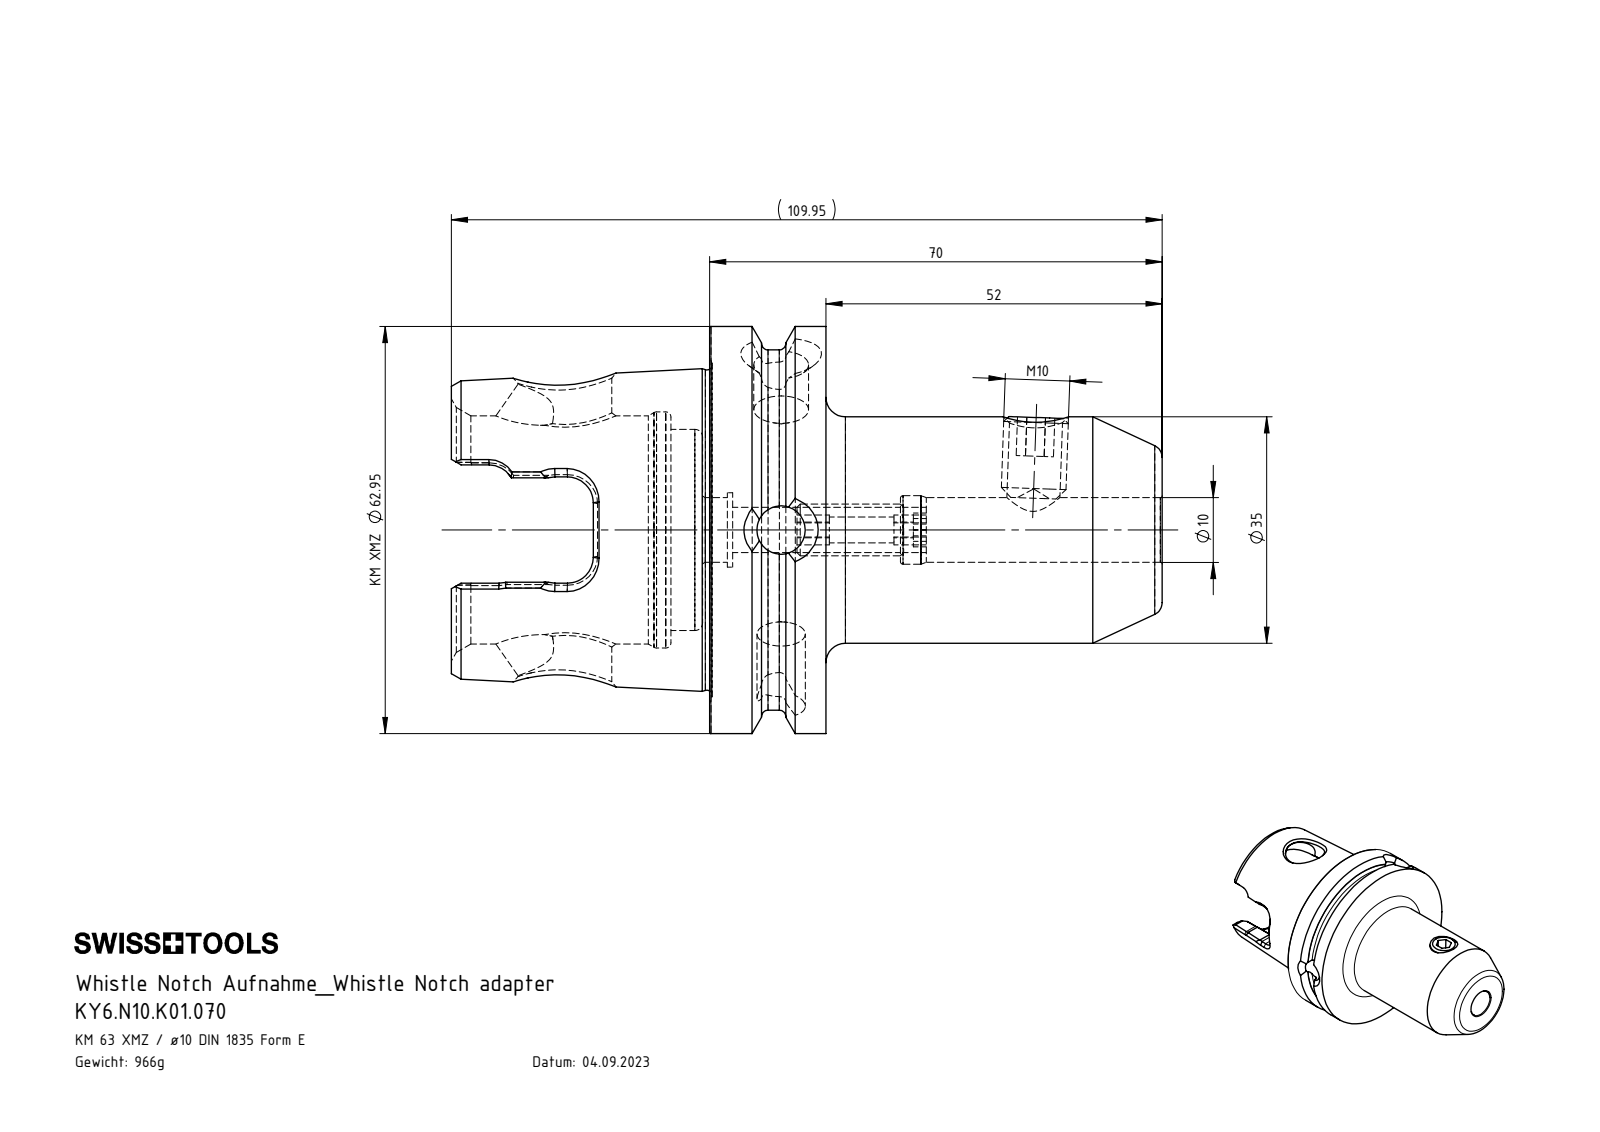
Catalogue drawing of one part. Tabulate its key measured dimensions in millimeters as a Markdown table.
| quantity | value |
| --- | --- |
| part name | KY6.N10.K01.070; ERU-AN3.K01.020_A; KY6-N10.K01.070_A; W10-ER1.001.012 |
| STEP written by | SolidWorks 2017 (AUTOMOTIVE_DESIGN) |
| units | millimeters |
| bodies | 3 solids, 285 faces (88 planar, 62 cylindrical, 135 other) |
| overall size | 109.95 × 62.95 × 62.95 |
| volume | 123 052 mm³ |
| surface area | 28 325 mm² |
| round holes (diameter × count) | 7.47 × 2, 4 × 1, 7 × 1, 8.2 × 1, 8.48 × 1, 10 × 1, 10.6 × 1, 11.5 × 1, 14.5 × 1, 31.1 × 1, 35.27 × 1, 36.5 × 1 |
| round bosses / shafts (diameter × count) | 62.95 × 1, 55.7 × 1, 35 × 1, 10 × 1, 8 × 1 |
| partial cylindrical surfaces (radius × count) | 4 × 6, 7.04 × 2 |
| main face-to-face distances | 18, 1.1, 19.1, 71.1, 70, 52, 6, 4.9, 24, 76 |
